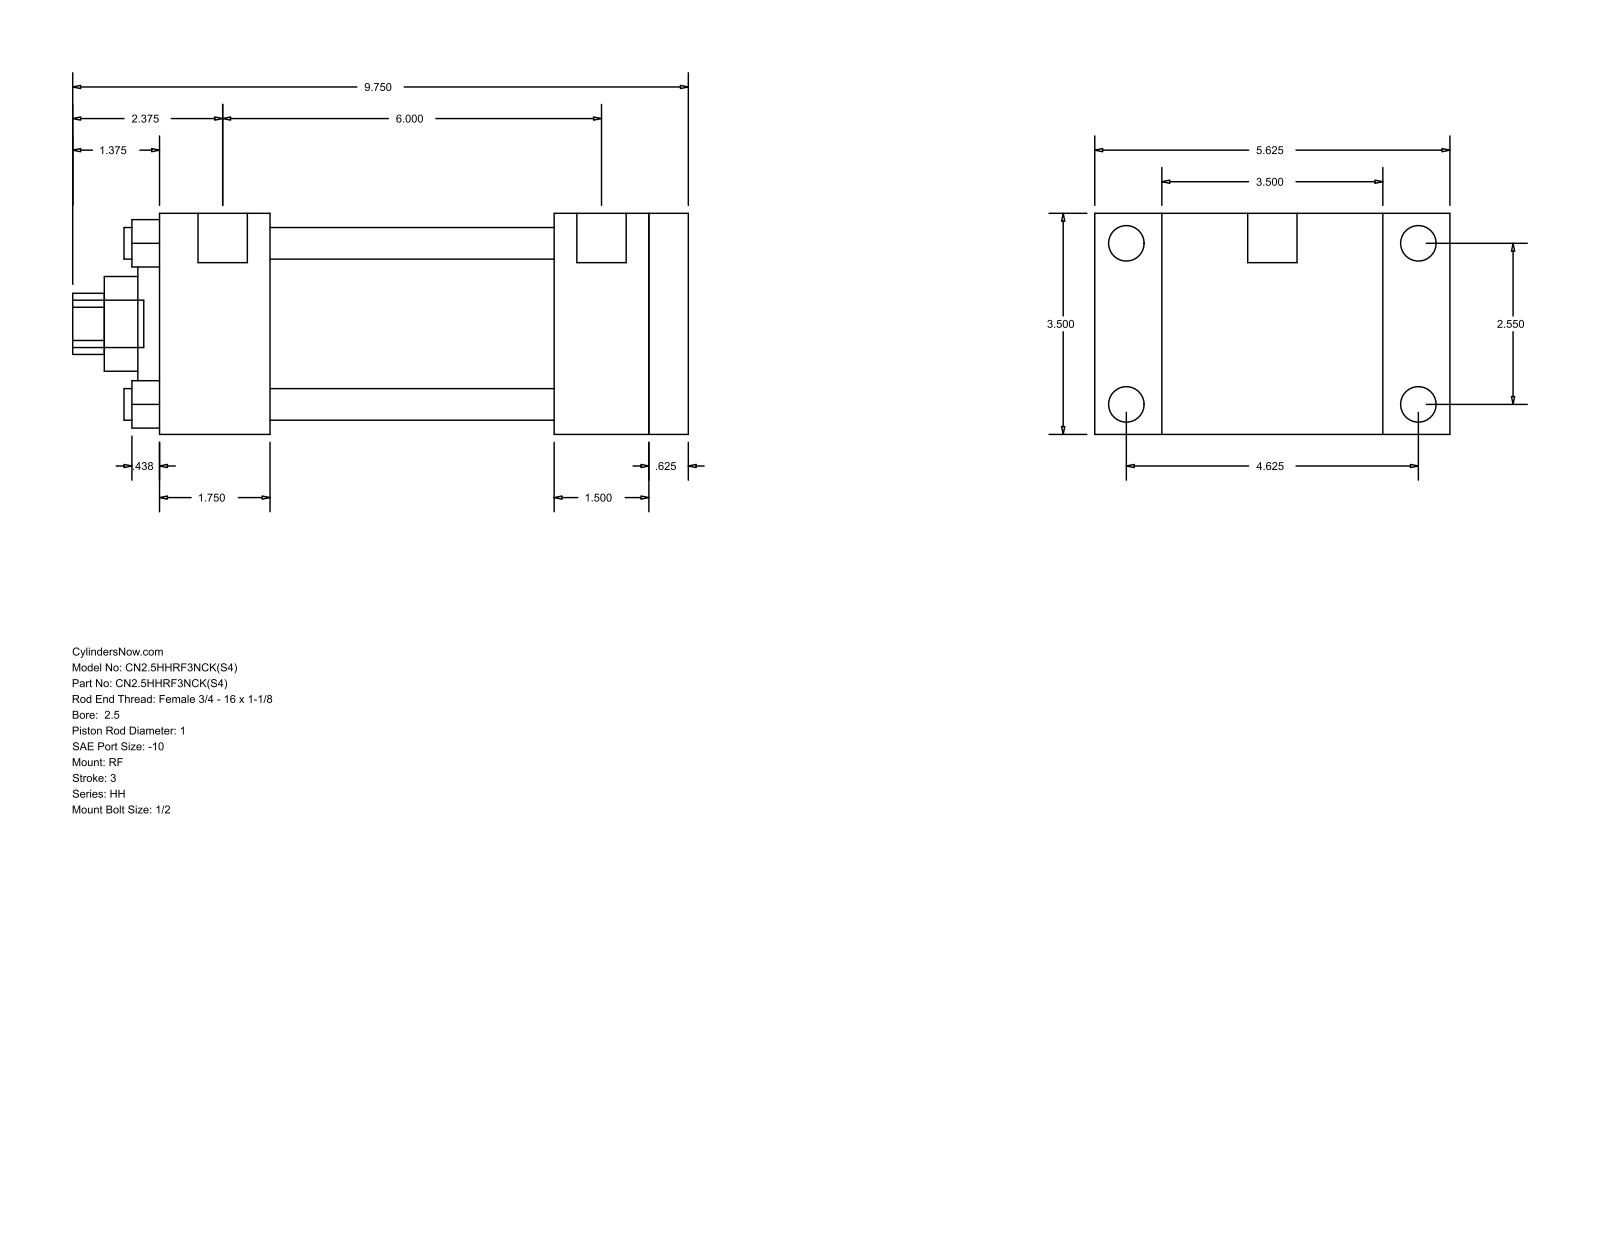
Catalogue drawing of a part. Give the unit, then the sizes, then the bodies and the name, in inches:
Units: inches
Overall size (bounding box): 9.75 × 5.625 × 3.5
Round holes (diameter × count): ⌀0.5 ×4, ⌀1 ×1, ⌀1.5 ×1, ⌀2.375 ×1, ⌀2.875 ×1
Round bosses / shafts (diameter × count): ⌀0.563 ×4, ⌀0.219 ×4, ⌀0.781 ×2, ⌀0.75 ×1
Partial cylindrical surfaces — rounded edges, fillets, slot ends (radius × count): R0.484 ×1
Main face-to-face distances: 3.5, 0.625, 7.75, 8.375, 1.75, 6, 6.625, 6.25, 4.5, 1.5
Hole centre spacings: 1.803, 2.55, 3.606
Bodies: 0 solids, 94 faces (65 planar, 29 cylindrical, 0 other)
Part name (STEP PRODUCT): HH_RF__0250_1
STEP written by: GSSL Pune (CONFIG_CONTROL_DESIGN)
